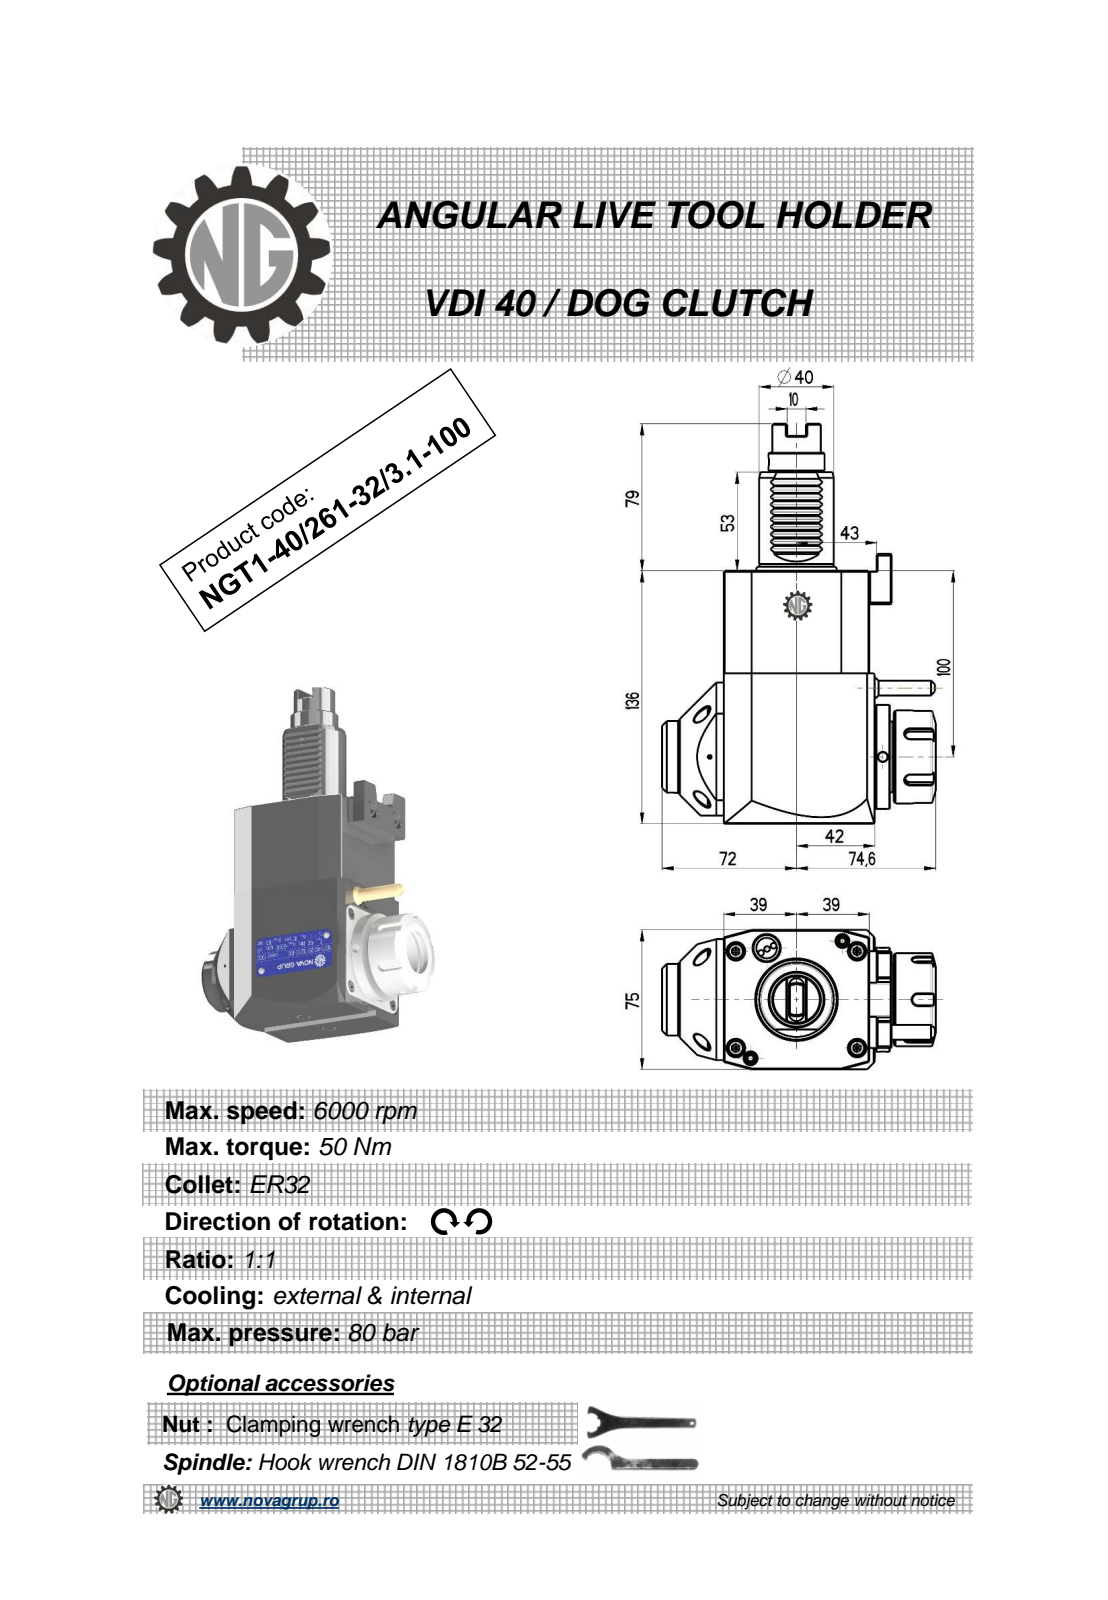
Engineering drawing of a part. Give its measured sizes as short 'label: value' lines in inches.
name: NGT1_40_261_32_3_1_100
written by: PRO/ENGINEER BY PARAMETRIC TECHNOLOGY CORPORATION, 2010280 (CONFIG_CONTROL_DESIGN)
unit: in
bodies: 1 solid, 379 faces (192 planar, 70 cylindrical, 117 other)
size: 8.465 × 5.772 × 2.953
volume: 62.92 in³; area: 122.7 in²
holes: 3× ⌀0.197, 1× ⌀0.118, 1× ⌀0.165, 1× ⌀1.063
bosses: 1× ⌀2.205, 1× ⌀1.969, 1× ⌀1.693, 1× ⌀1.614, 1× ⌀1.575, 1× ⌀1.516, 1× ⌀1.181, 1× ⌀1.024
rounds: 10× R0.012, 6× R0.009, 5× R0.118, 3× R0.02, 2× R0.039, 1× R0.492, 1× R1.575
face distances: 2.953, 5.354, 3.071, 3.189, 0.118, 0.02, 3.342, 0.039, 3.181, 0.11
hole spacings: 1.611, 4.833, 6.24
